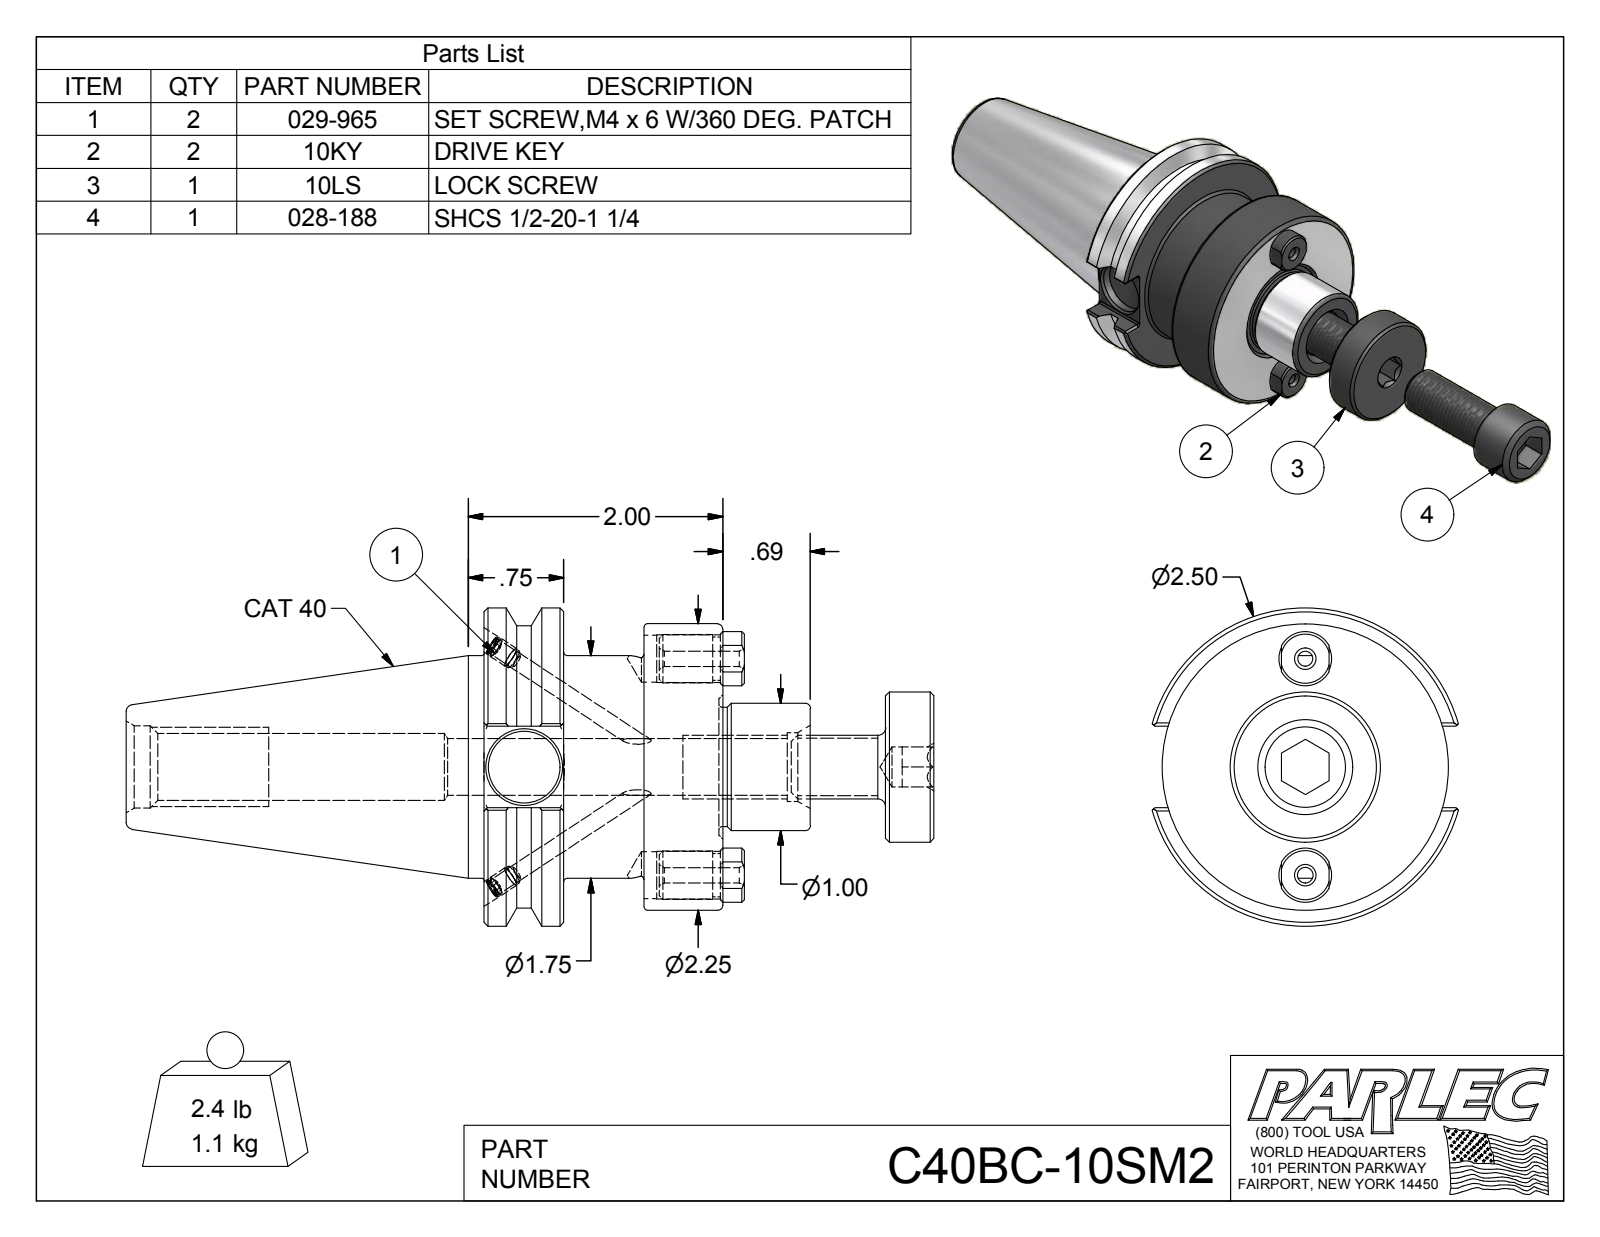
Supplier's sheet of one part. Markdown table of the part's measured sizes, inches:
| quantity | value |
| --- | --- |
| part name | C40BC-10SM2; C40BC-10SM2-1; 10KY; 10LS (+2 more) |
| STEP written by | Autodesk Inventor 2012 (AUTOMOTIVE_DESIGN) |
| units | inches |
| bodies | 7 solids, 216 faces (91 planar, 58 cylindrical, 67 other) |
| overall size | 8.522 × 2.5 × 2.406 |
| volume | 11.28 in³ |
| surface area | 61.2 in² |
| round holes (diameter × count) | 0.12 × 2, 0.13 × 2, 0.161 × 2, 0.368 × 2, 0.374 × 2, 0.312 × 1, 0.315 × 1, 0.399 × 1, 0.446 × 1, 0.527 × 1, 0.54 × 1, 0.648 × 1 |
| round bosses / shafts (diameter × count) | 0.38 × 2, 0.34 × 2, 0.165 × 2, 0.157 × 2, 2.5 × 1, 2.25 × 1, 2.219 × 1, 1.75 × 1 |
| partial cylindrical surfaces (radius × count) | 0.02 × 12, 0.214 × 2 |
| main face-to-face distances | 1.25, 1.875, 0.625, 1.255, 0.63, 0.62, 3.534, 2.909, 2.279, 1.659 |
| hole center spacings | 0.85, 1.7 |
